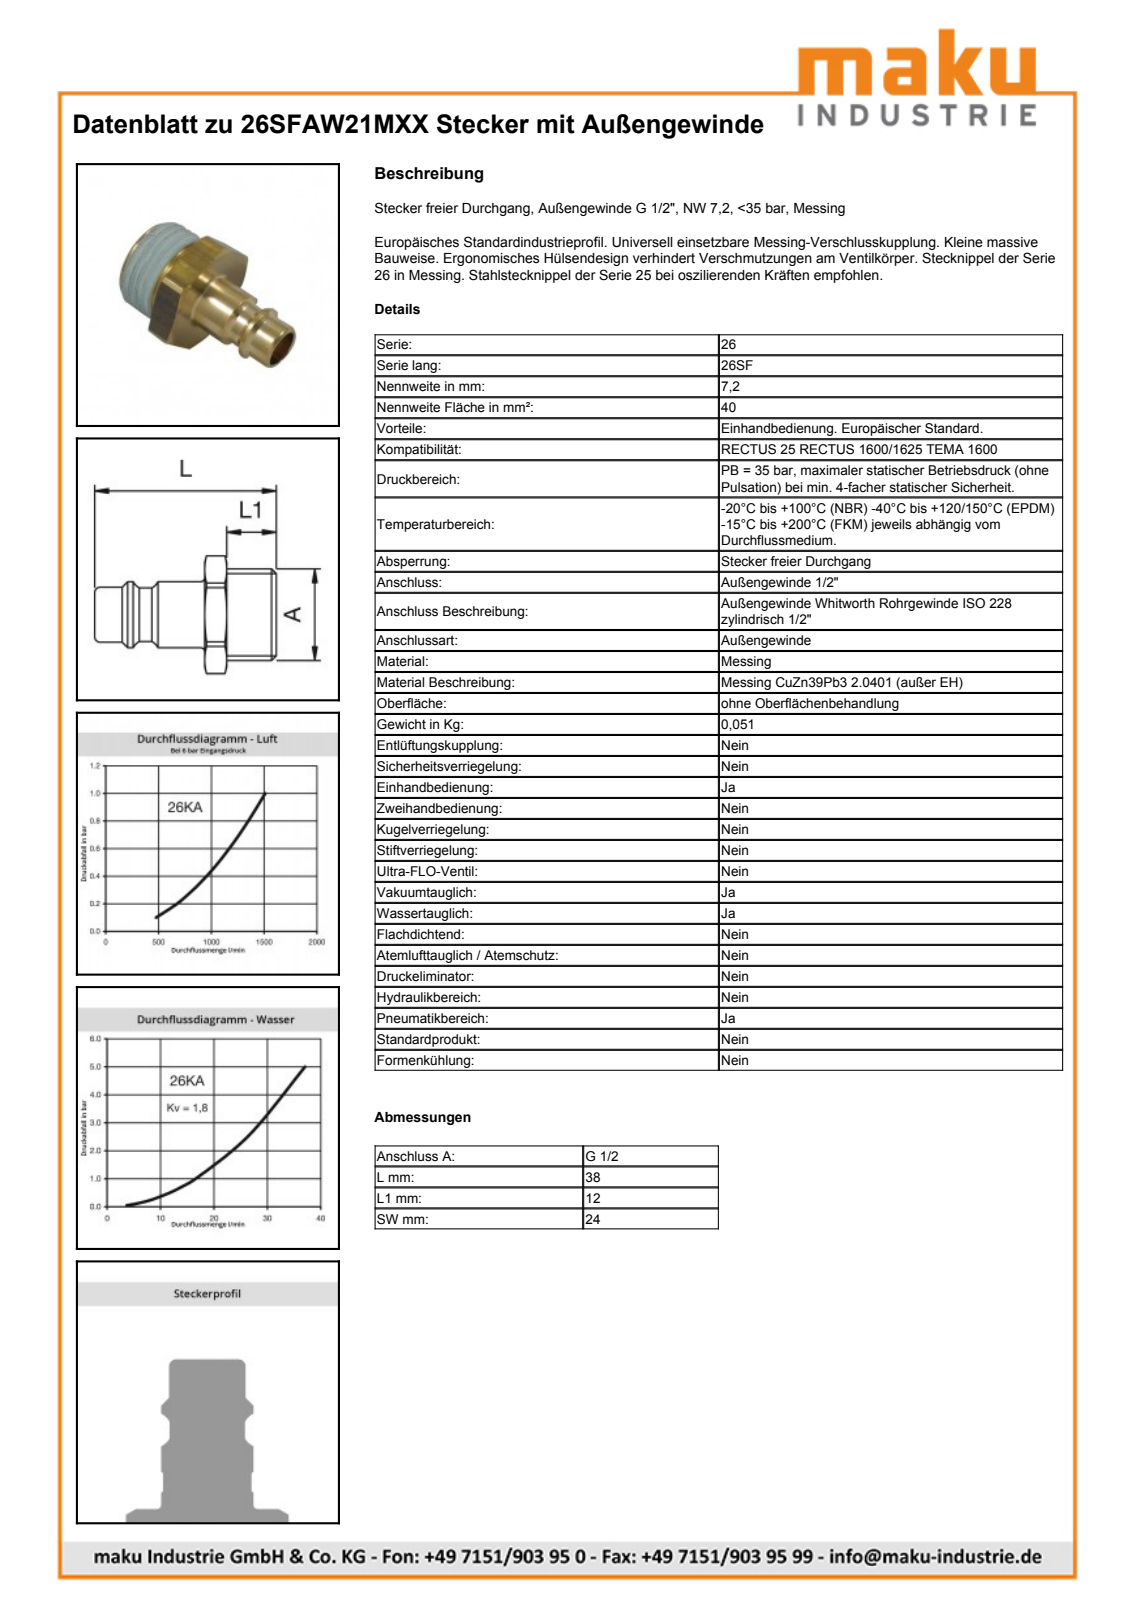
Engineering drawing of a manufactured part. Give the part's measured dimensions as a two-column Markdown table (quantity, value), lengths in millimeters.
| quantity | value |
| --- | --- |
| part name | D105864 |
| STEP written by | Autodesk Inventor 2011 (AUTOMOTIVE_DESIGN) |
| units | millimeters |
| bodies | 1 solid, 41 faces (10 planar, 12 cylindrical, 19 other) |
| overall size | 38 × 27.05 × 24 |
| volume | 6 563 mm³ |
| surface area | 3 729 mm² |
| round holes (diameter × count) | 7.85 × 1 |
| round bosses / shafts (diameter × count) | 20.95 × 1, 12 × 1, 10 × 1, 9.75 × 1 |
| partial cylindrical surfaces (radius × count) | 13.53 × 1 |
| main face-to-face distances | 24, 6, 18, 12, 20, 26, 38 |
